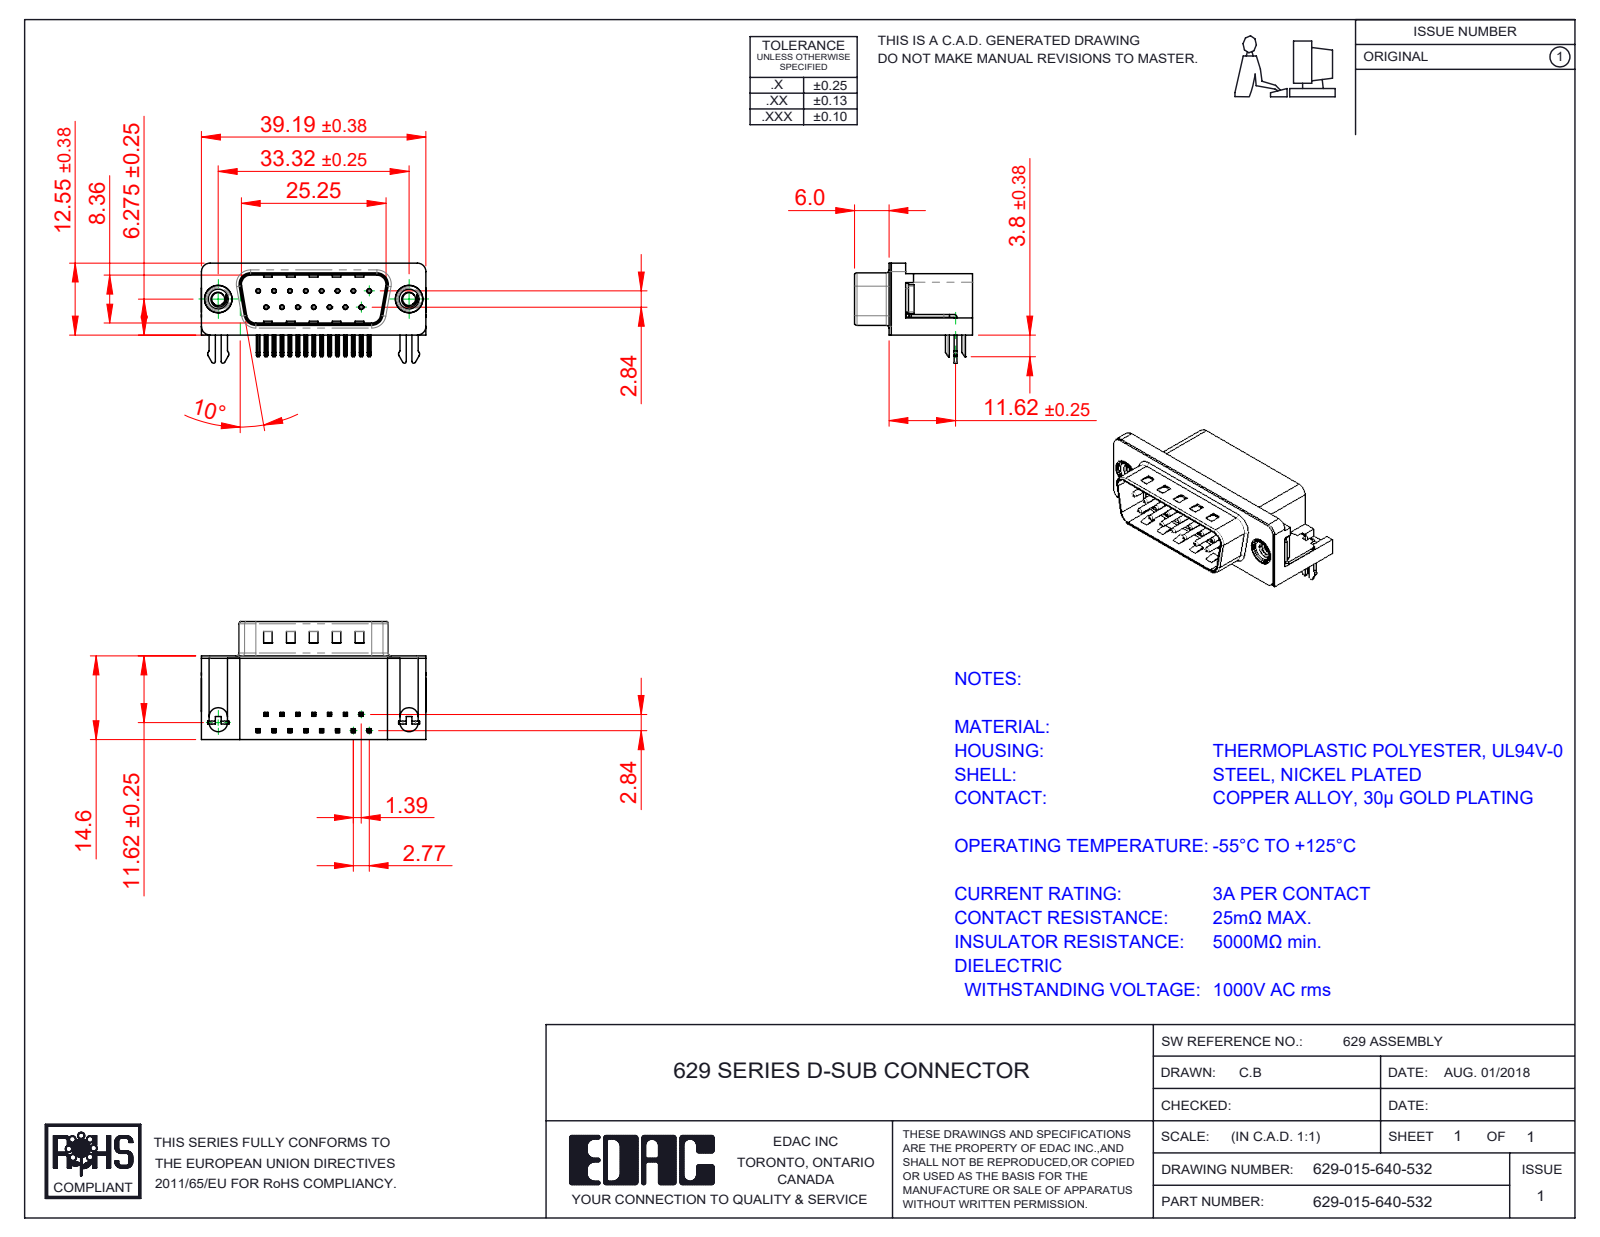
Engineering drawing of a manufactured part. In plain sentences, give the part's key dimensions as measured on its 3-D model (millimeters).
The part is named "629 Shell_15 Socket; 629 Contact Bottom; 629 2 Prong Board Lock; 629 4-40 Threaded Rivet (+3 more)". Its 3-D file was written by "SolidWorks 2020 (CONFIG_CONTROL_DESIGN)". It is 21 solids with 1515 faces: 923 planar, 453 cylindrical and 139 other. Overall it measures 39.22 by 20.6 by 17.48 millimeters. Its volume is 5 081 cubic millimeters and its surface area 6 079 square millimeters. Round holes: 15 of diameter 0.35, 15 of diameter 0.8, 2 of diameter 2.26, 2 of diameter 4, 2 of diameter 4.8, 2 of diameter 5. Round bosses or shafts: 15 of diameter 0.75, 2 of diameter 4.9, 2 of diameter 4.75, 2 of diameter 3.9. Partial cylindrical surfaces (rounded edges, fillets, slot ends): 68 of radius 0.25, 30 of radius 0.12, 16 of radius 1, 14 of radius 0.5, 8 of radius 1.6, 6 of radius 1.5, 4 of radius 0.32, 4 of radius 0.9. The main face-to-face distances are 0.4, 14.2, 10.35, 2.1, 14.6, 10.46, 1.7, 10.86, 8.76, 0.5. The hole center spacings are 3.16, 2.77, 5.54, 8.31, 11.08, 5.03, 5.04, 7.48.
